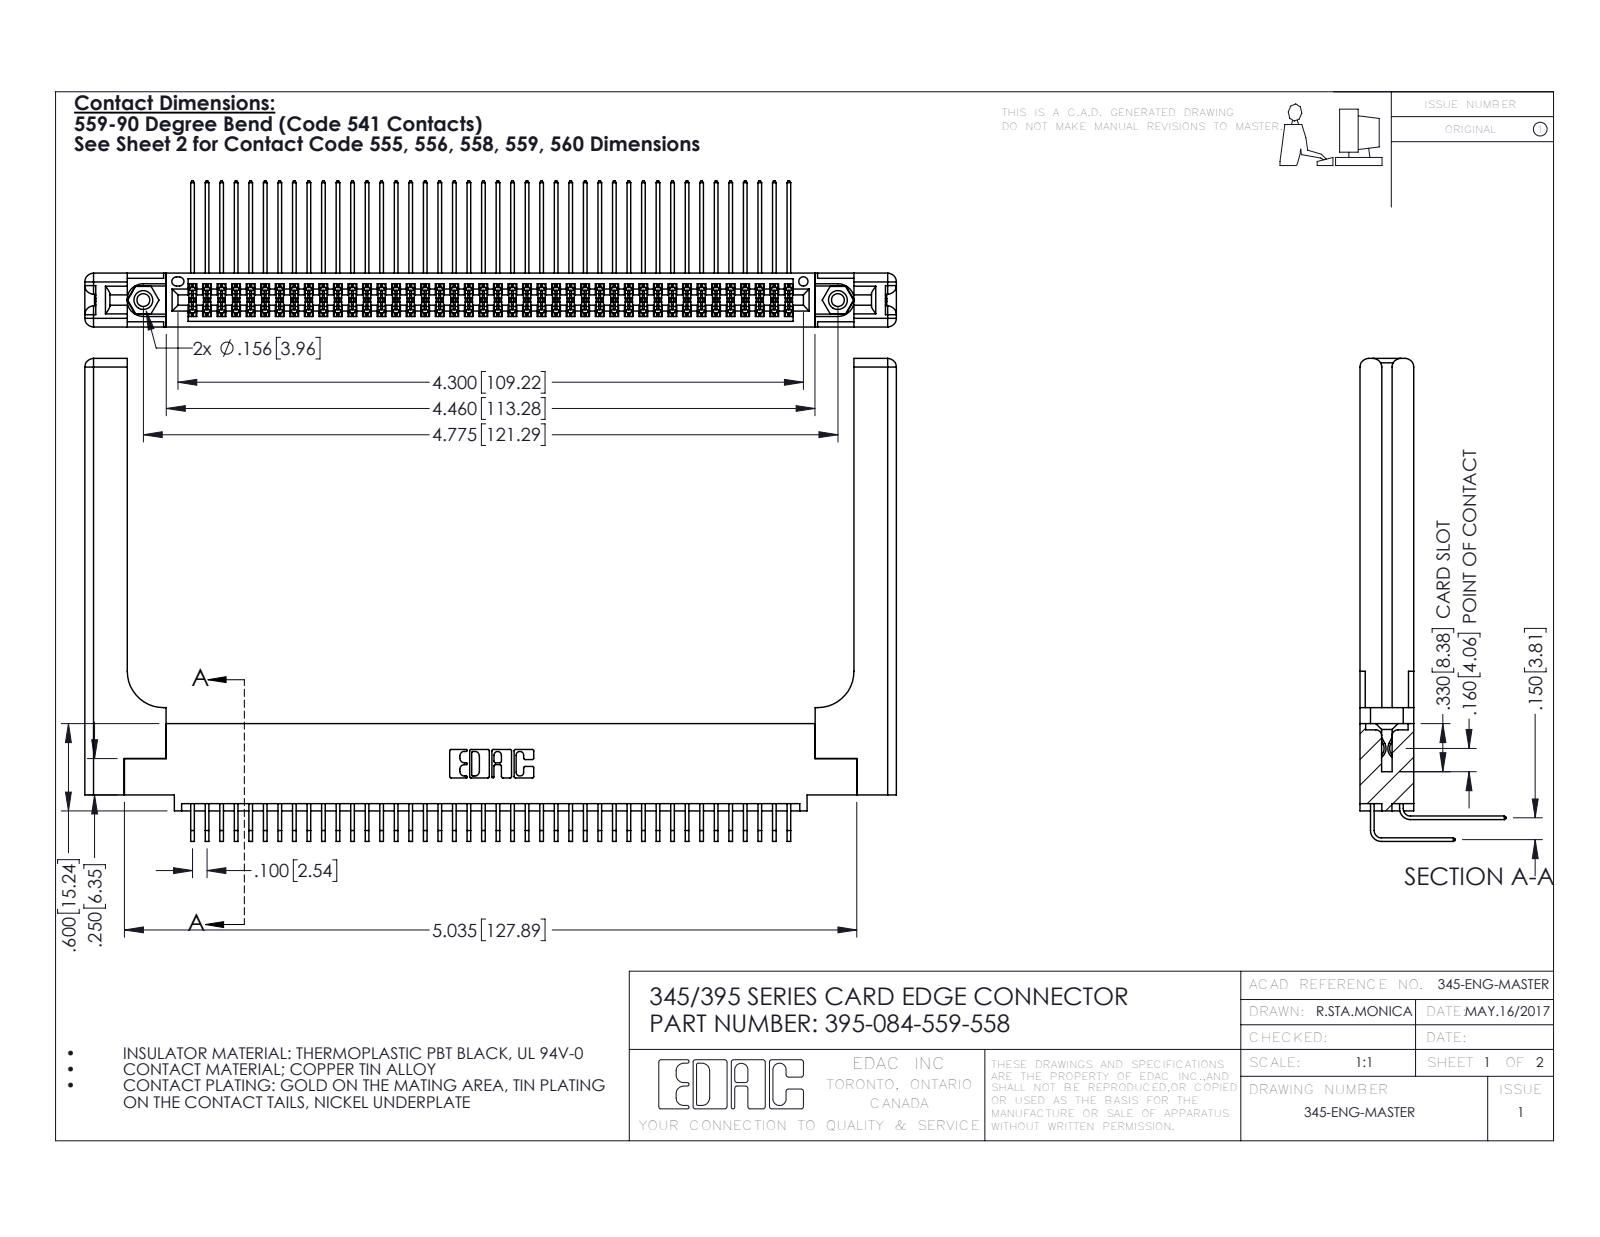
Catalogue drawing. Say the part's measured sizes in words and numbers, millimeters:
The part is named "345-292-001_559 Tail - 2; 395-084-559-558; 345-220-058_345-220-058; 345 Part_0.110 Offset - 0.156 Dia-TH (+2 more)". Its 3-D file was written by "SolidWorks 2016 (CONFIG_CONTROL_DESIGN)". It is 89 solids with 4754 faces: 3172 planar, 1522 cylindrical and 60 other. Overall it measures 141.7 by 84.3 by 25.5 millimeters. Its volume is 22 650 cubic millimeters and its surface area 28 390 square millimeters. Round holes: 2 of diameter 2.3, 2 of diameter 3.2, 2 of diameter 4, 1 of diameter 1.6. Round bosses or shafts: 2 of diameter 3.9. Partial cylindrical surfaces (rounded edges, fillets, slot ends): 126 of radius 0.2, 22 of radius 0.3, 16 of radius 1.5, 6 of radius 0.2, 6 of radius 0.8, 3 of radius 0.7, 2 of radius 0.4, 2 of radius 0.5. The main face-to-face distances are 1.8, 9.4, 7.6, 2.5, 6.9, 0.6, 5.1, 5.7, 4.4, 3.8. The hole center spacings are 6.9, 115.3, 121.3.
